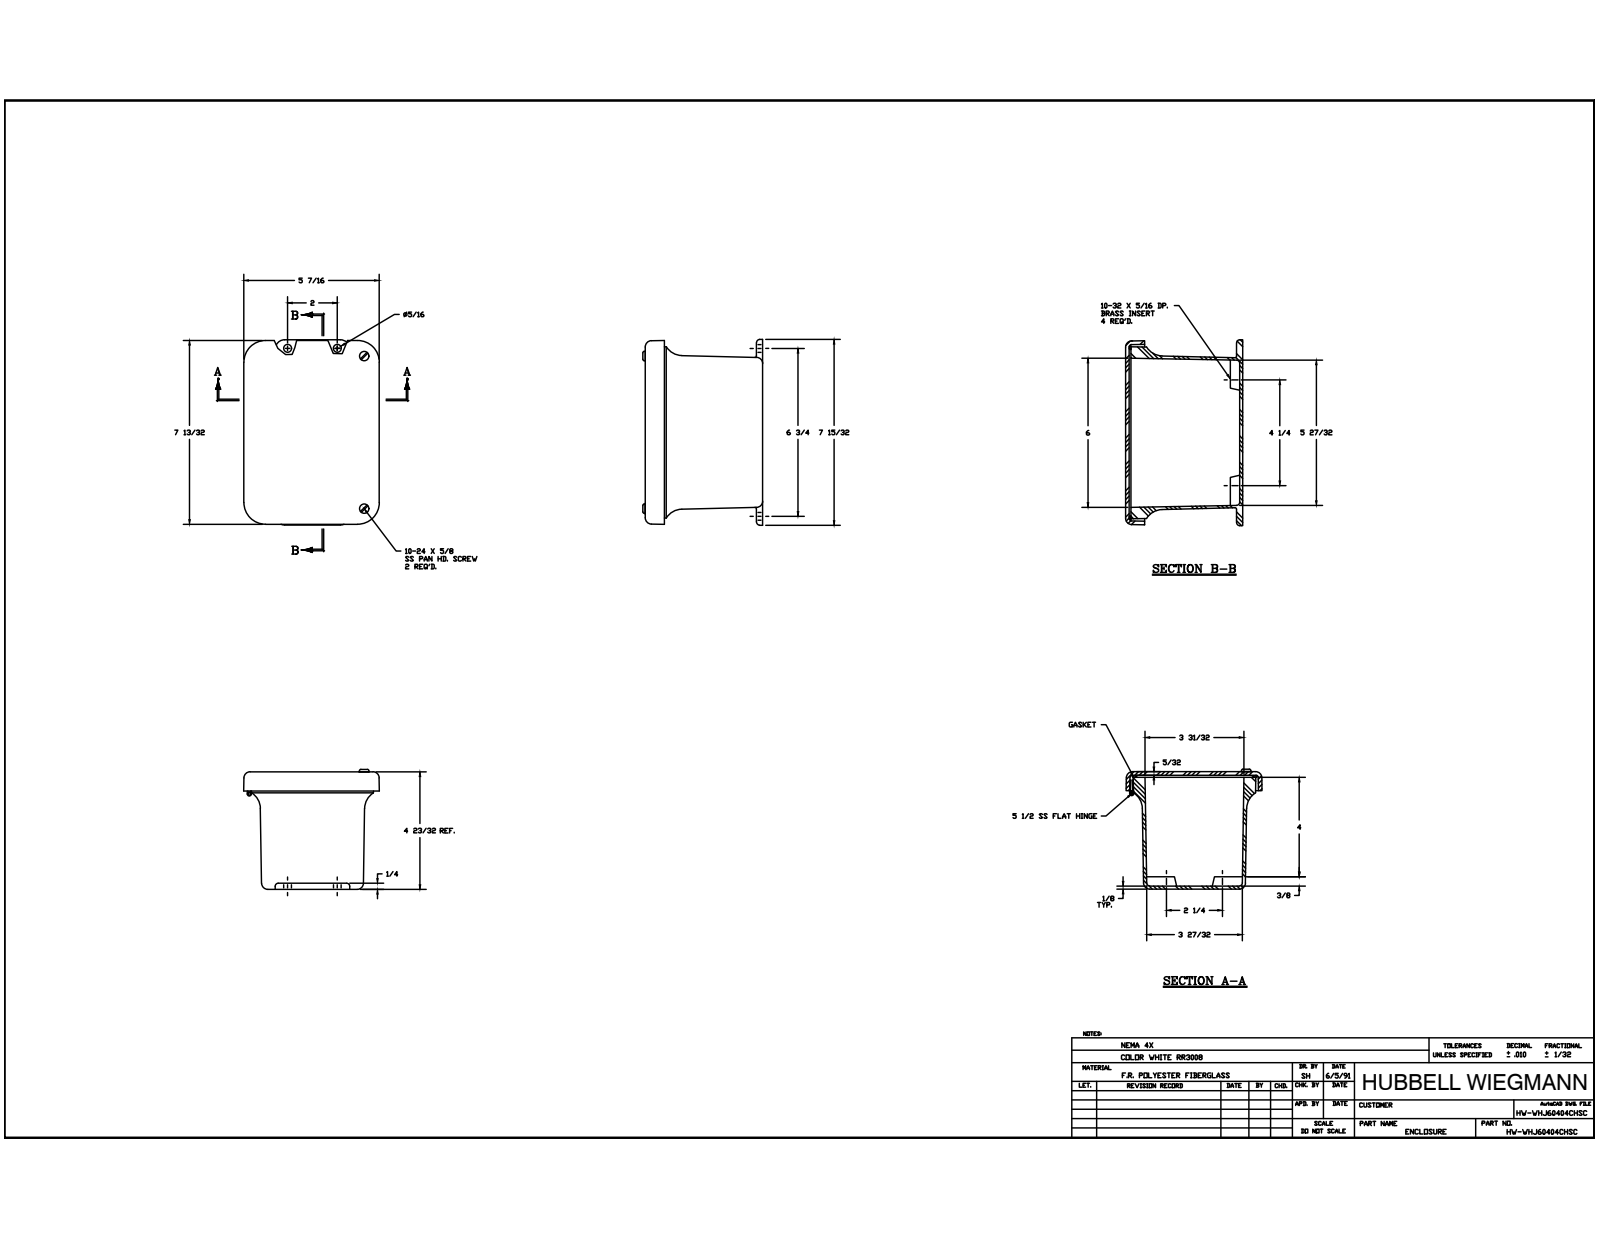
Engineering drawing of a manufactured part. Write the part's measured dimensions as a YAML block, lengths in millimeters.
part_name: "J604HW_1; RMINS45821P_9; RMINS45821P_10; RMINS45821P_11 (+8 more)"
step_written_by: "Autodesk Inventor 2014 (AUTOMOTIVE_DESIGN)"
units: millimeters
bodies: {solids: 19, faces: 645, planar: 200, cylindrical: 243, other: 202}
overall_size: [189.85, 139.28, 123.16]
volume: 512898
surface_area: 253691
round_holes:
  - {diameter: 3.33, count: 5}
  - {diameter: 3.56, count: 5}
  - {diameter: 3.86, count: 5}
  - {diameter: 3.96, count: 4}
  - {diameter: 5.54, count: 4}
  - {diameter: 3.68, count: 2}
  - {diameter: 2.16, count: 1}
round_bosses_or_shafts:
  - {diameter: 6.86, count: 6}
  - {diameter: 6.35, count: 5}
  - {diameter: 3.17, count: 5}
  - {diameter: 4.83, count: 2}
  - {diameter: 3.97, count: 2}
  - {diameter: 3.94, count: 1}
partial_cylinders:
  - {radius: 0.79, count: 20}
  - {radius: 3.17, count: 12}
  - {radius: 6.35, count: 8}
  - {radius: 5.08, count: 4}
  - {radius: 9.53, count: 4}
  - {radius: 19.05, count: 4}
  - {radius: 1.6, count: 2}
face_to_face_distances: [3.68, 116.15, 119.83, 3.18, 112.97, 116.65, 114.3, 5.53, 111.12, 1.85]
hole_center_spacings: [63.5, 84.81, 12.7, 34.07, 50.8, 57.14, 101.6, 105.56]
